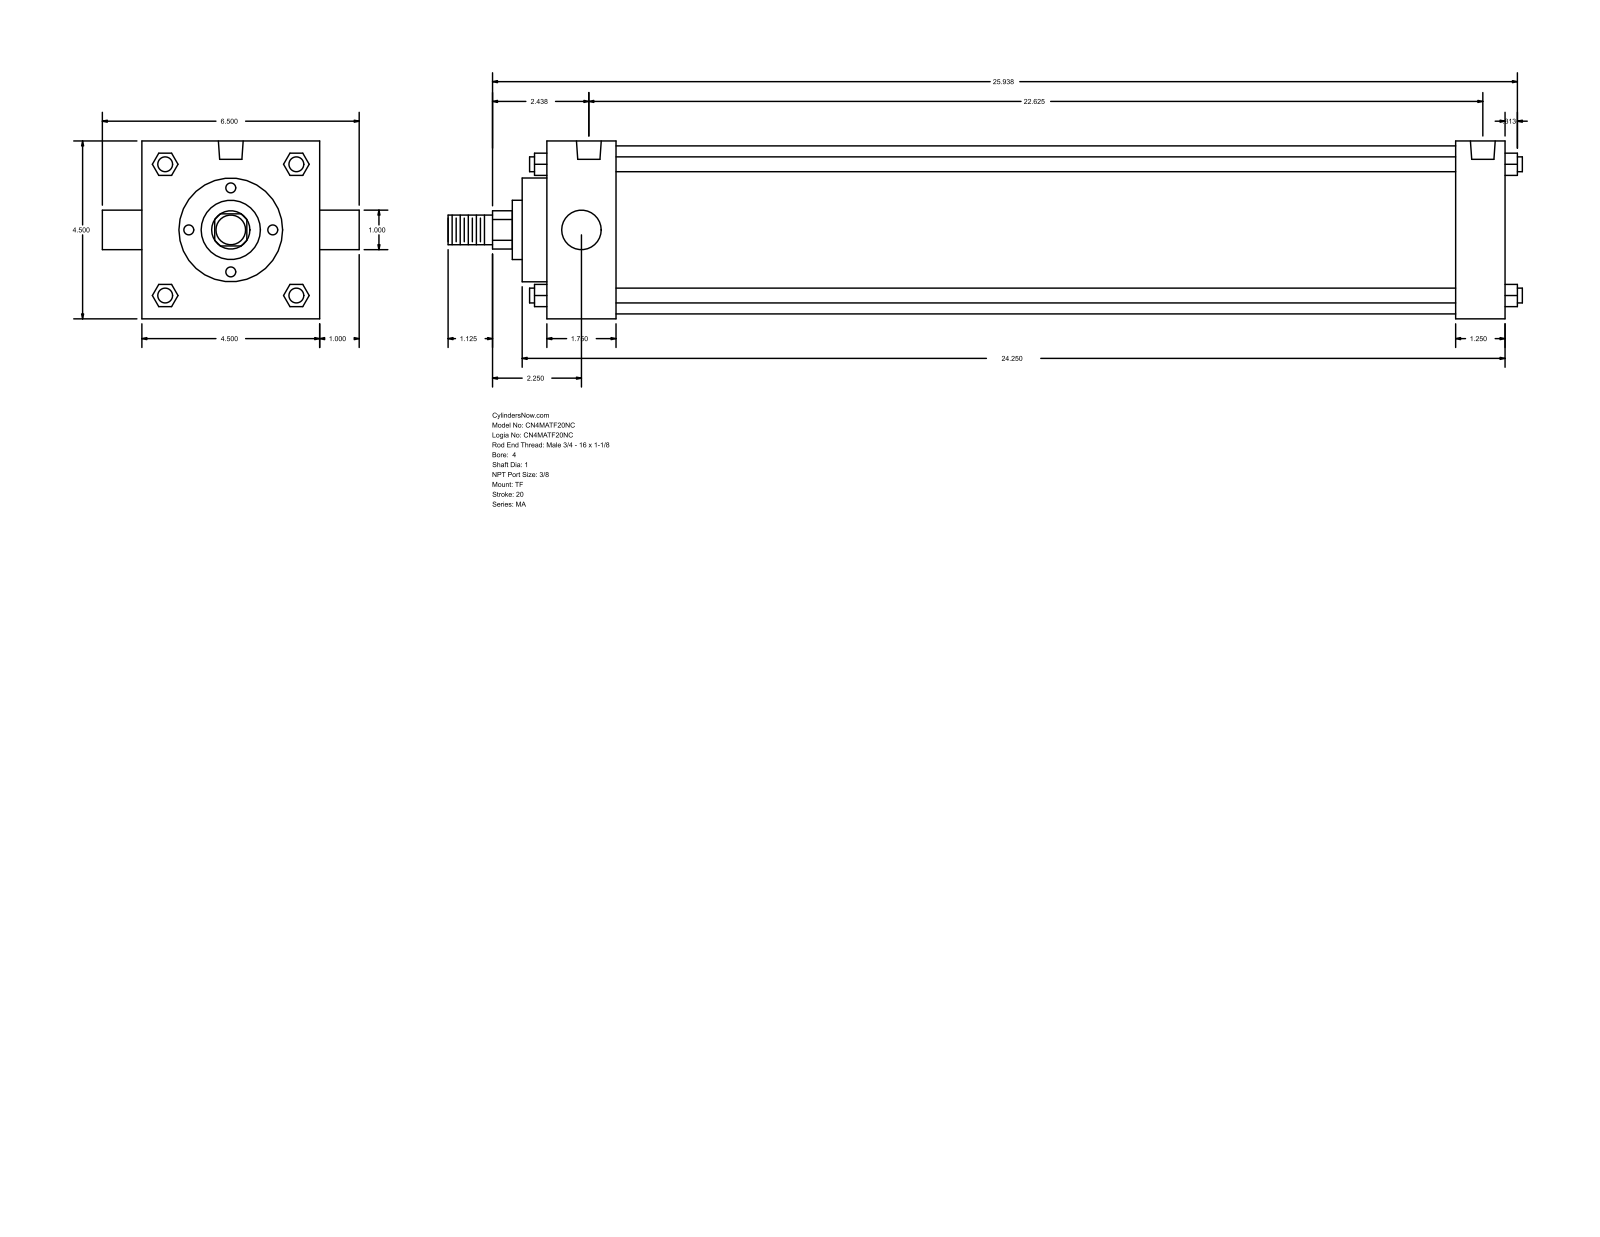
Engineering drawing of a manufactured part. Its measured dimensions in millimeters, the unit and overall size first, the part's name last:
Units: millimetres
Overall size (bounding box): 690.56 × 165.1 × 114.3
Round holes (diameter × count): ⌀11.11 ×3, ⌀15.93 ×2
Round bosses / shafts (diameter × count): ⌀9.53 ×4, ⌀25.4 ×2, ⌀107.95 ×1, ⌀66.67 ×1, ⌀38.1 ×1, ⌀19.05 ×1
Partial cylindrical surfaces — rounded edges, fillets, slot ends (radius × count): R12.29 ×1
Main face-to-face distances: 114.3, 615.96, 584.2, 31.76, 44.46, 539.74, 571.5, 15.87, 60.33, 600.07
Hole centre spacings: 4.76, 569.92, 565.16, 574.68
Bodies: 0 solids, 122 faces (93 planar, 29 cylindrical, 0 other)
Part name (STEP PRODUCT): MA_TF__0400_1
STEP written by: GSSL Pune (CONFIG_CONTROL_DESIGN)
